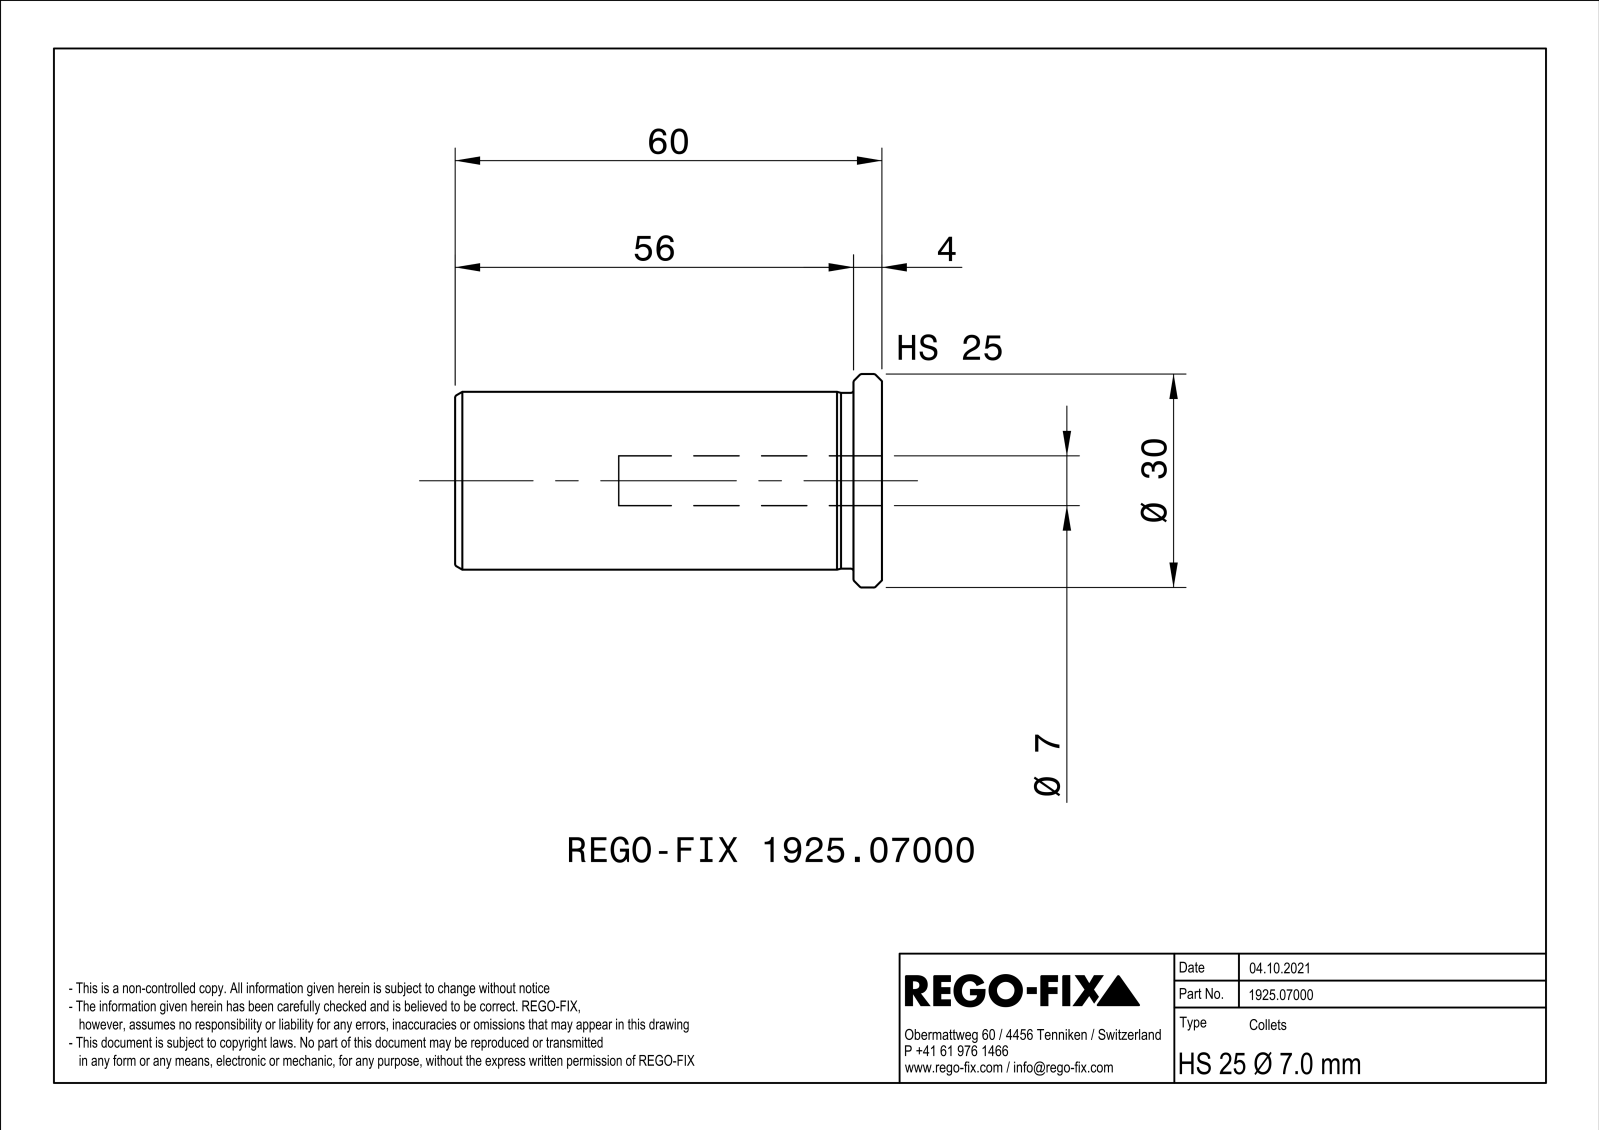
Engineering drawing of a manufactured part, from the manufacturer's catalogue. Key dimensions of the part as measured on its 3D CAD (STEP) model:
Part name (STEP PRODUCT): NOCUT
STEP written by: SIEMENS PLM Software Solid Edge ST10 (AUTOMOTIVE_DESIGN)
Units: millimetres
Bodies: 1 solid, 73 faces (22 planar, 12 cylindrical, 39 other)
Overall size (bounding box): 60 × 29.99 × 29.99
Volume: 23 006 mm³ · Surface area: 9 831 mm²
Round holes (diameter × count): ⌀7 ×1, ⌀10 ×1, ⌀20.5 ×1
Round bosses / shafts (diameter × count): ⌀30 ×1, ⌀25 ×1, ⌀24.7 ×1
Main face-to-face distances: 0.8, 4, 60, 56
